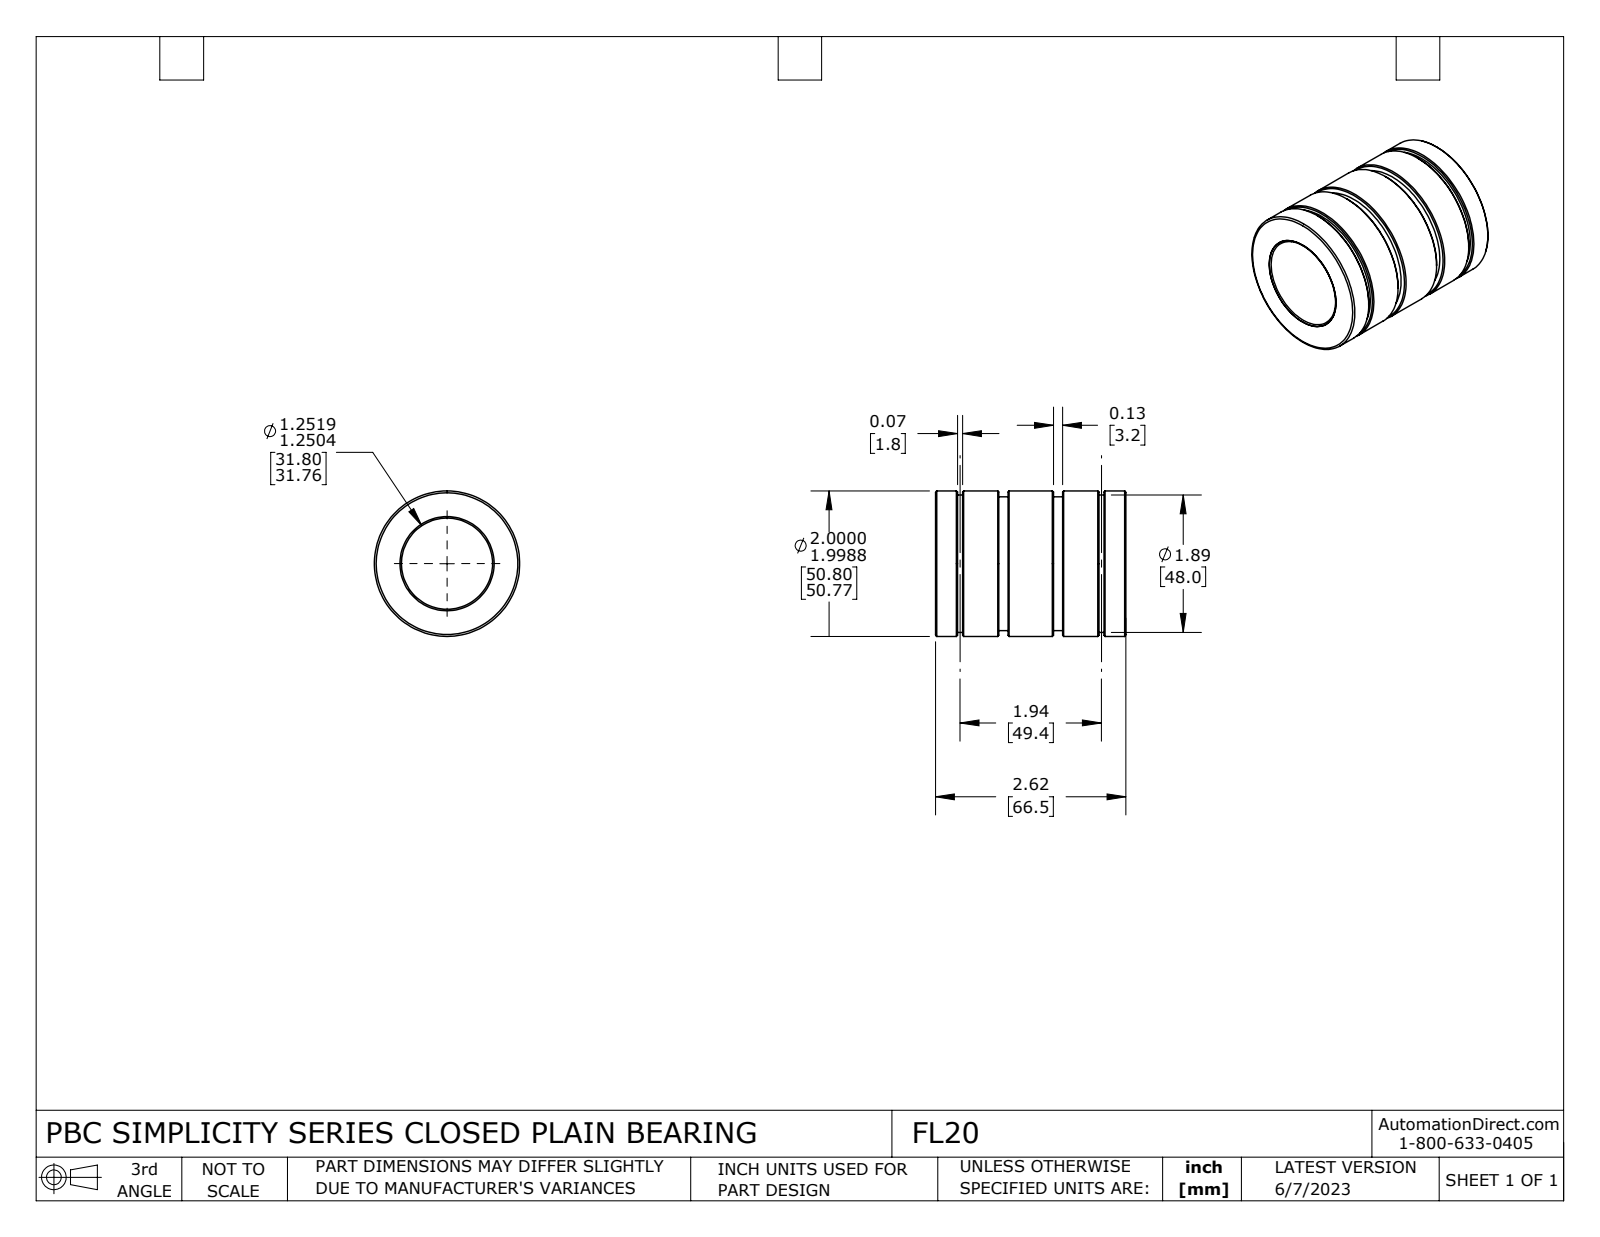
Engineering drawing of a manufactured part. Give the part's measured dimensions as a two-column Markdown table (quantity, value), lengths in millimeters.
| quantity | value |
| --- | --- |
| part name | FL20 |
| STEP written by | SolidWorks 2021 (CONFIG_CONTROL_DESIGN) |
| units | millimeters |
| bodies | 2 solids, 58 faces (10 planar, 24 cylindrical, 24 other) |
| overall size | 66.5 × 50.8 × 50.8 |
| volume | 78 950 mm³ |
| surface area | 35 030 mm² |
| round holes (diameter × count) | 31.8 × 1, 32.9 × 1 |
| round bosses / shafts (diameter × count) | 50.8 × 1, 48 × 1, 46.7 × 1 |
| main face-to-face distances | 66.5, 25.3, 41.2, 22.1, 44.4, 3.2, 19.1, 7.7, 58.8, 14.5 |
